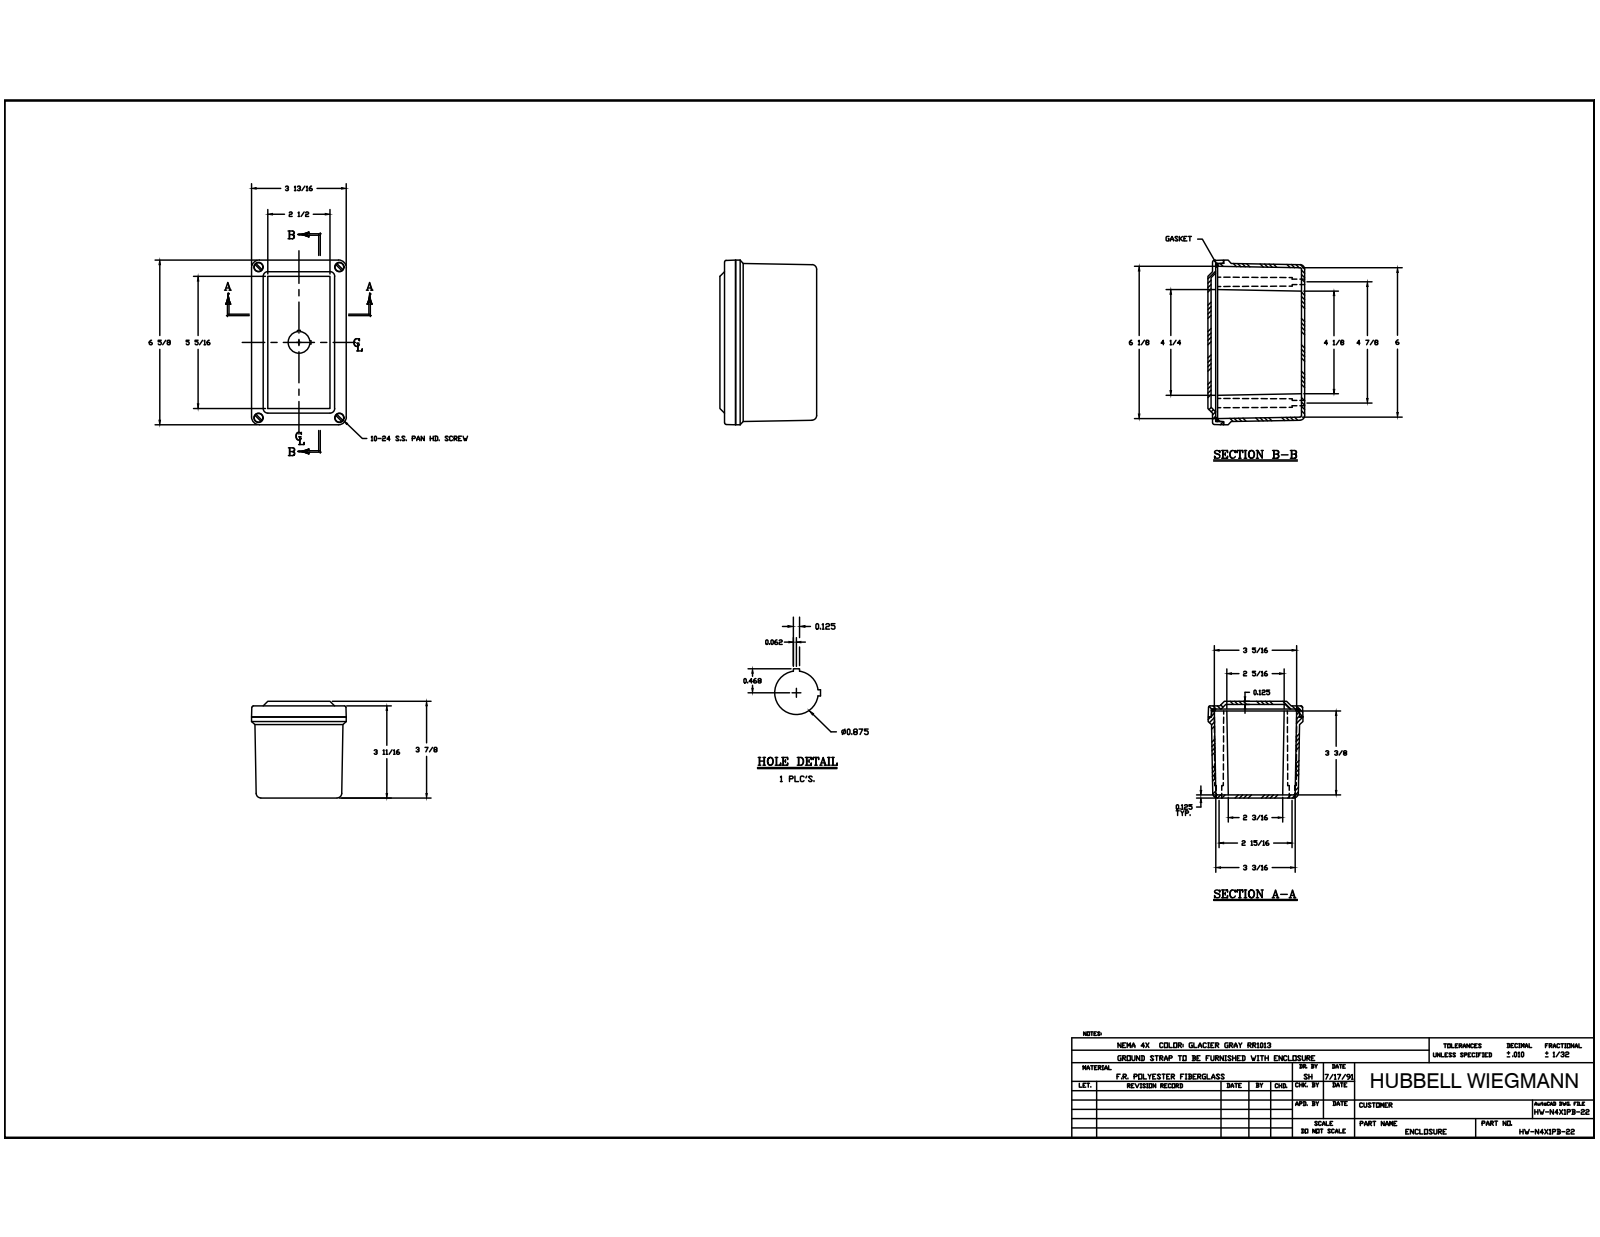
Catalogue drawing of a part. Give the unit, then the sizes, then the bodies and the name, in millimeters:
Units: millimetres
Overall size (bounding box): 168.28 × 98.42 × 96.84
Round holes (diameter × count): ⌀5.56 ×8, ⌀3.68 ×4, ⌀4.83 ×4, ⌀9.52 ×4, ⌀22.22 ×1
Round bosses / shafts (diameter × count): ⌀9.42 ×4, ⌀5.54 ×4, ⌀4.5 ×4
Partial cylindrical surfaces — rounded edges, fillets, slot ends (radius × count): R0.79 ×20, R0.3 ×16, R7.94 ×8, R1.59 ×4, R4.47 ×4, R4.76 ×4, R5.59 ×4, R8.26 ×4
Main face-to-face distances: 3.17, 3.42, 95.25, 4.76, 90.49, 12.7, 98.42, 92.08, 1.59, 87.32
Hole centre spacings: 82.54, 15.59, 15.6, 72.28, 80.01, 80.02, 87.35, 87.36
Volume: 334 953 mm³ · Surface area: 172 157 mm²
Bodies: 11 solids, 387 faces (189 planar, 106 cylindrical, 92 other)
Part name (STEP PRODUCT): WPCF644 BOX; 10-24 X 0.4375 DP BRASS INSERT; WPCF1PB22 CVR; WPCF644 GASKET (+3 more)
STEP written by: Autodesk Inventor 2014 (AUTOMOTIVE_DESIGN)
